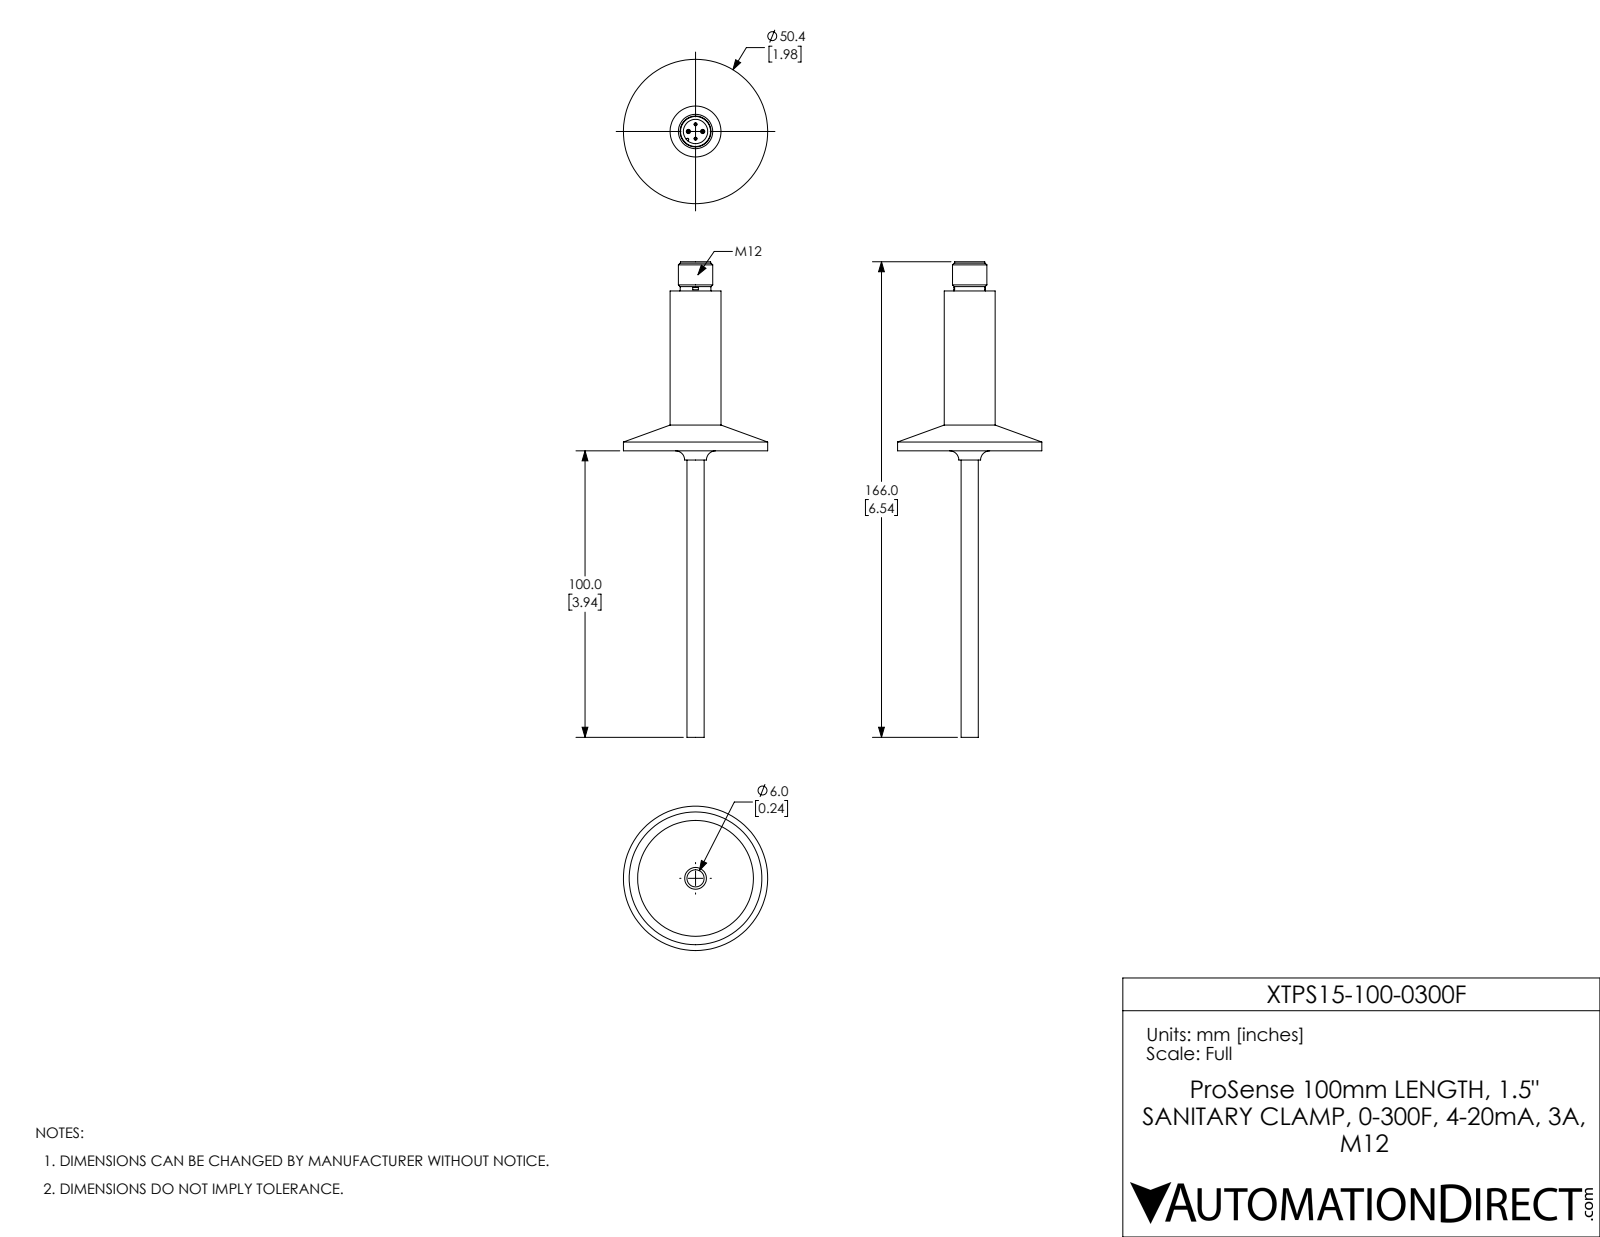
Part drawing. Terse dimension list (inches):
name: XTPS15-100-0300F
written by: SolidWorks 2017 (AUTOMOTIVE_DESIGN)
unit: in
bodies: 1 solid, 79 faces (26 planar, 23 cylindrical, 30 other)
size: 6.536 × 1.984 × 1.984
volume: 1.629 in³; area: 15.5 in²
holes: 1× ⌀0.335
bosses: 4× ⌀0.04, 1× ⌀1.984, 1× ⌀0.701, 1× ⌀0.472, 1× ⌀0.421, 1× ⌀0.413, 1× ⌀0.236
rounds: 1× R0.016
face distances: 2.198, 2.245, 0.048, 2.599, 0.402, 0.354, 3.937, 6.135, 6.182, 6.536
